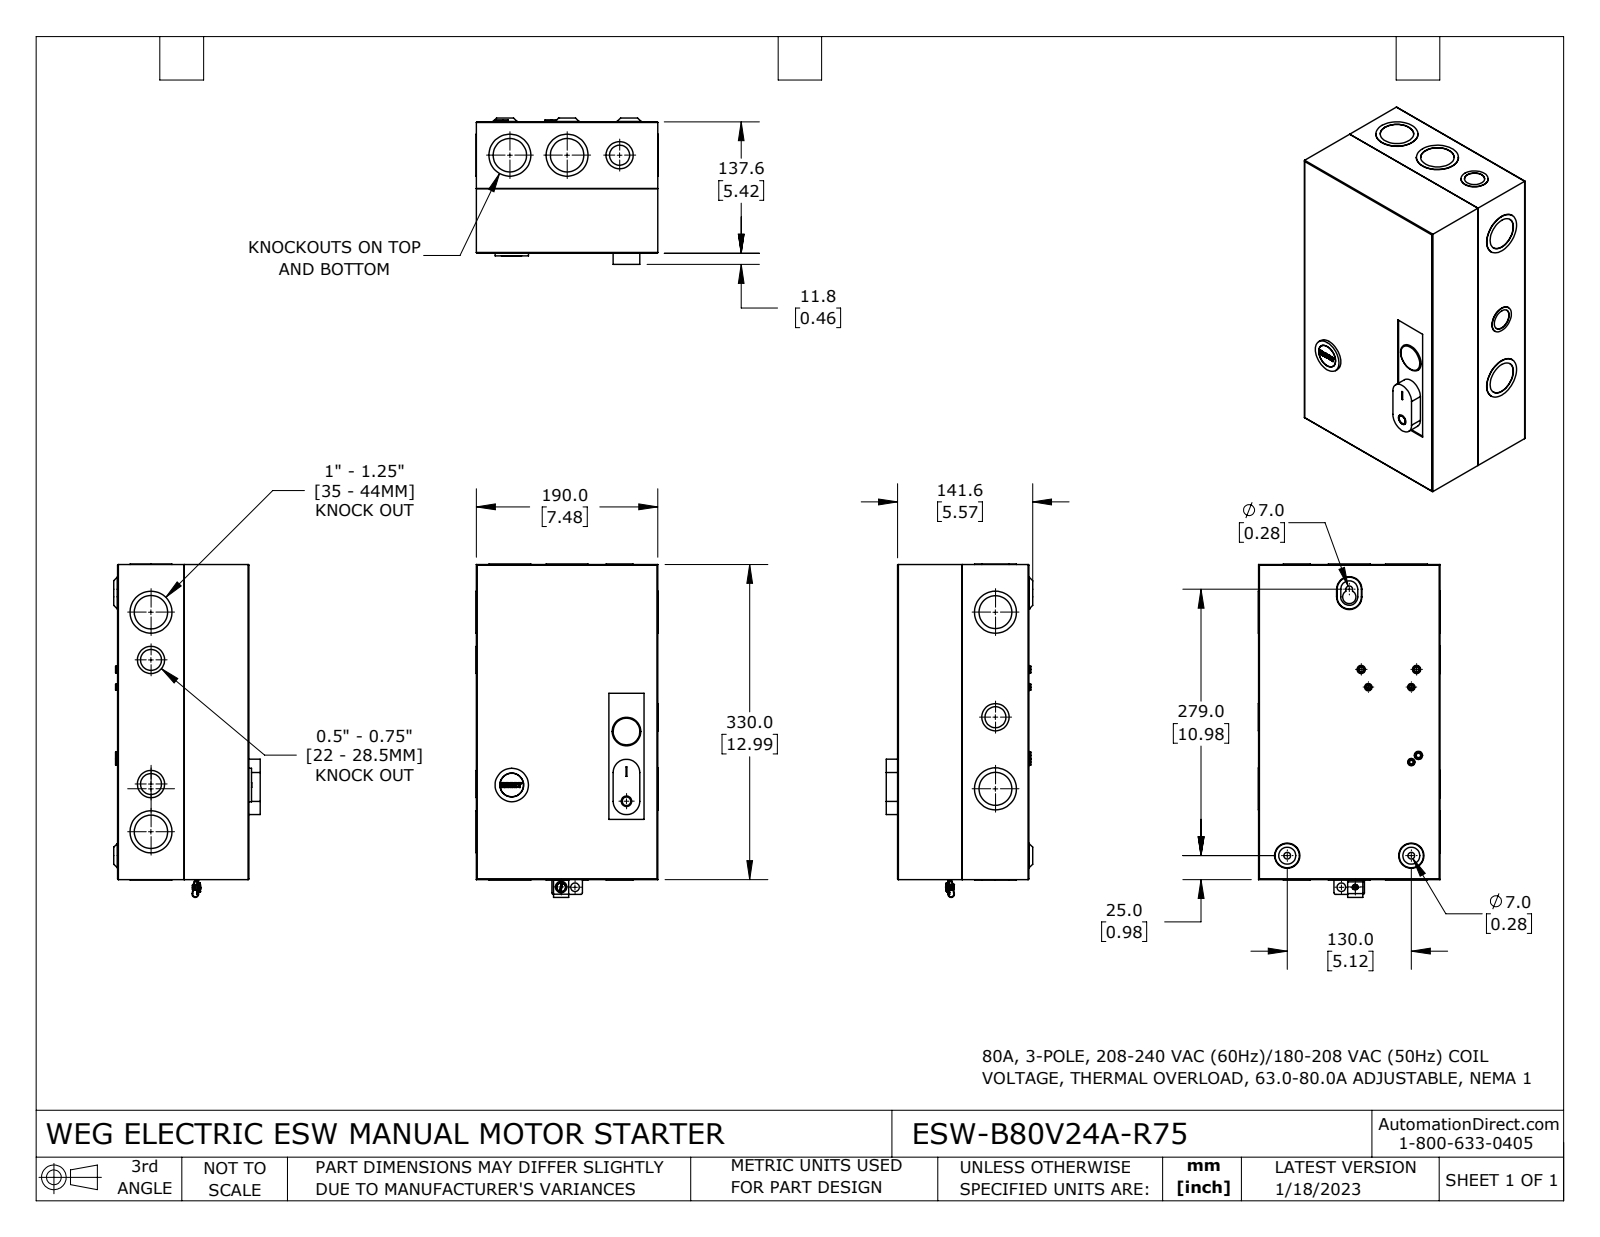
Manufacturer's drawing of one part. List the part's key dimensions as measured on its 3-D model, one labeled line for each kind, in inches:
Part name (STEP PRODUCT): ESW-B80V24A-R75
STEP written by: SolidWorks 2021 (CONFIG_CONTROL_DESIGN)
Units: inches
Bodies: 7 solids, 435 faces (161 planar, 221 cylindrical, 53 other)
Overall size (bounding box): 13.74 × 7.504 × 6.039
Volume: 24.58 in³ · Surface area: 936.7 in²
Round holes (diameter × count): ⌀1.378 ×4, ⌀0.146 ×3, ⌀0.183 ×3, ⌀0.276 ×2, ⌀0.866 ×2, ⌀0.886 ×2, ⌀1.357 ×2, ⌀0.256 ×1, ⌀0.279 ×1, ⌀0.354 ×1, ⌀0.433 ×1, ⌀0.469 ×1
Round bosses / shafts (diameter × count): ⌀1.732 ×4, ⌀1.122 ×3, ⌀0.278 ×3, ⌀0.24 ×3, ⌀1.734 ×2, ⌀1.378 ×1, ⌀1.193 ×1, ⌀1.148 ×1
Partial cylindrical surfaces — rounded edges, fillets, slot ends (radius × count): R0.004 ×34, R0.031 ×8, R0.079 ×3, R0.138 ×3, R0.059 ×2, R0.075 ×2, R0.108 ×2, R0.122 ×2
Main face-to-face distances: 0.047, 5.37, 7.433, 5.323, 5.417, 12.945, 7.386, 7.48, 0.071, 12.898
Hole centre spacings: 0.571, 1.772, 1.969, 2.283, 2.362, 5.118, 7.087, 10.972
